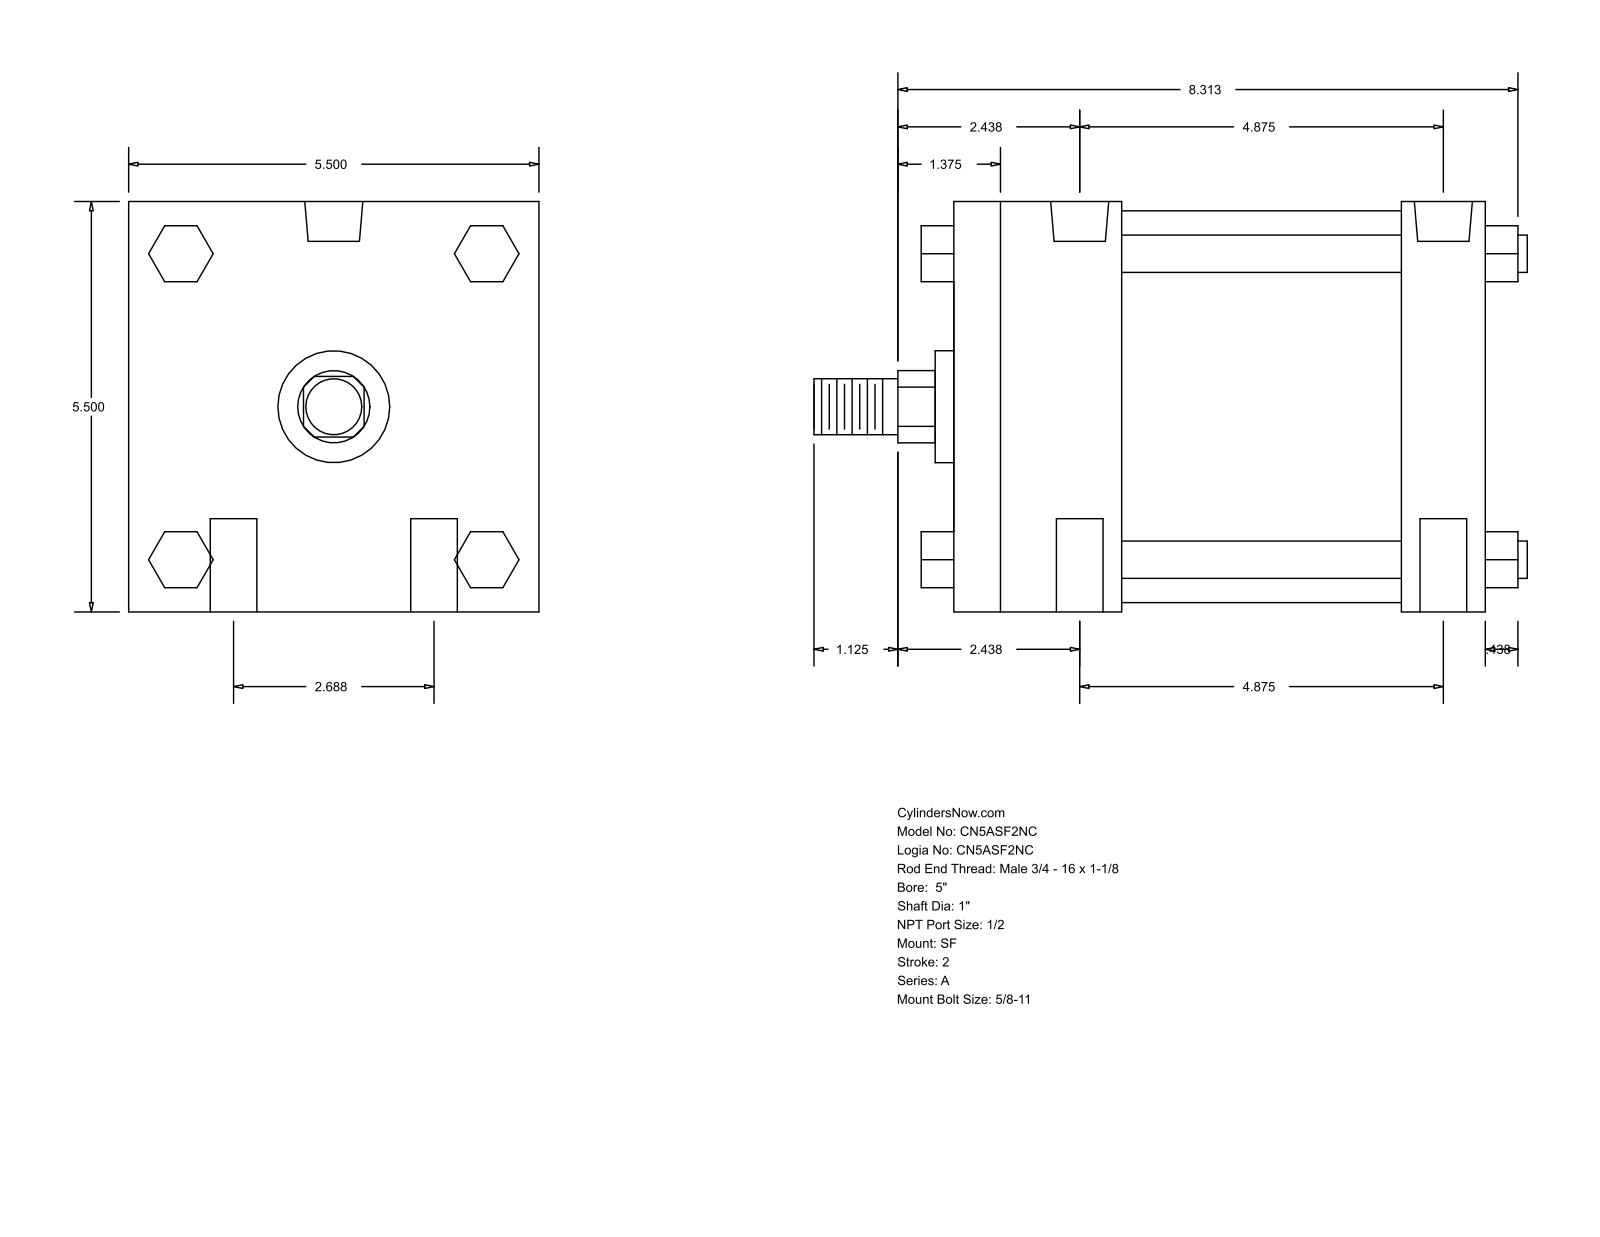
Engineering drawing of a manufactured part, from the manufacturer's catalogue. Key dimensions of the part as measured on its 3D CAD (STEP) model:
Part name (STEP PRODUCT): A_SF__0500_1
STEP written by: GSSL Pune (CONFIG_CONTROL_DESIGN)
Units: millimetres
Bodies: 0 solids, 124 faces (94 planar, 30 cylindrical, 0 other)
Overall size (bounding box): 242.89 × 139.7 × 139.7
Round holes (diameter × count): ⌀15.88 ×4, ⌀8.73 ×2, ⌀19.77 ×2
Round bosses / shafts (diameter × count): ⌀12.7 ×4, ⌀133.35 ×1, ⌀38.1 ×1, ⌀25.4 ×1, ⌀19.05 ×1
Partial cylindrical surfaces — rounded edges, fillets, slot ends (radius × count): R12.29 ×1
Main face-to-face distances: 139.7, 180.98, 57.15, 152.4, 95.25, 123.83, 28.58, 19.05, 52.07, 90.18
Hole centre spacings: 34.13, 128.45, 123.83, 68.26, 141.4, 119.05
